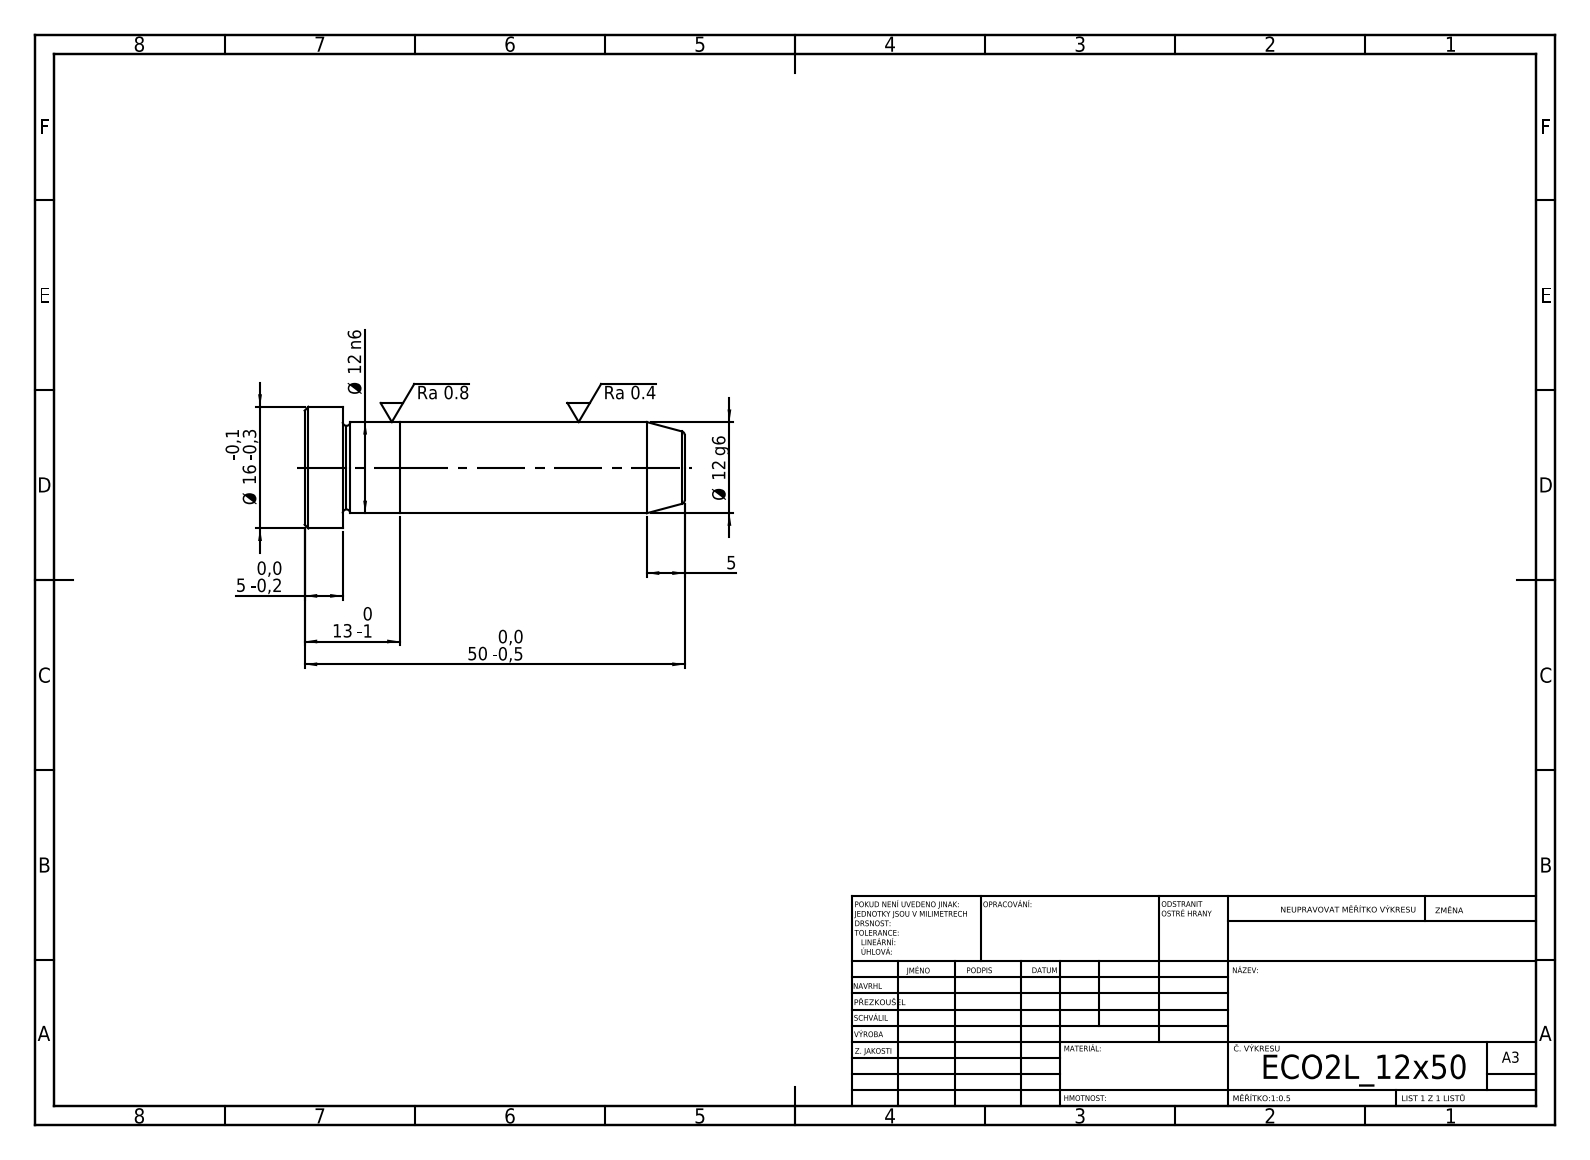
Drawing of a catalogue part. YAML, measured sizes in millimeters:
step_written_by: "SolidWorks 2019 (CONFIG_CONTROL_DESIGN)"
units: millimeters
bodies: {solids: 2, faces: 21, planar: 5, cylindrical: 6, other: 10}
overall_size: [50, 16, 16]
volume: 5957
surface_area: 2516
round_bosses_or_shafts:
  - {diameter: 16, count: 1}
  - {diameter: 12, count: 1}
face_to_face_distances: [12.5, 7.5, 5, 37.5, 45, 50]
